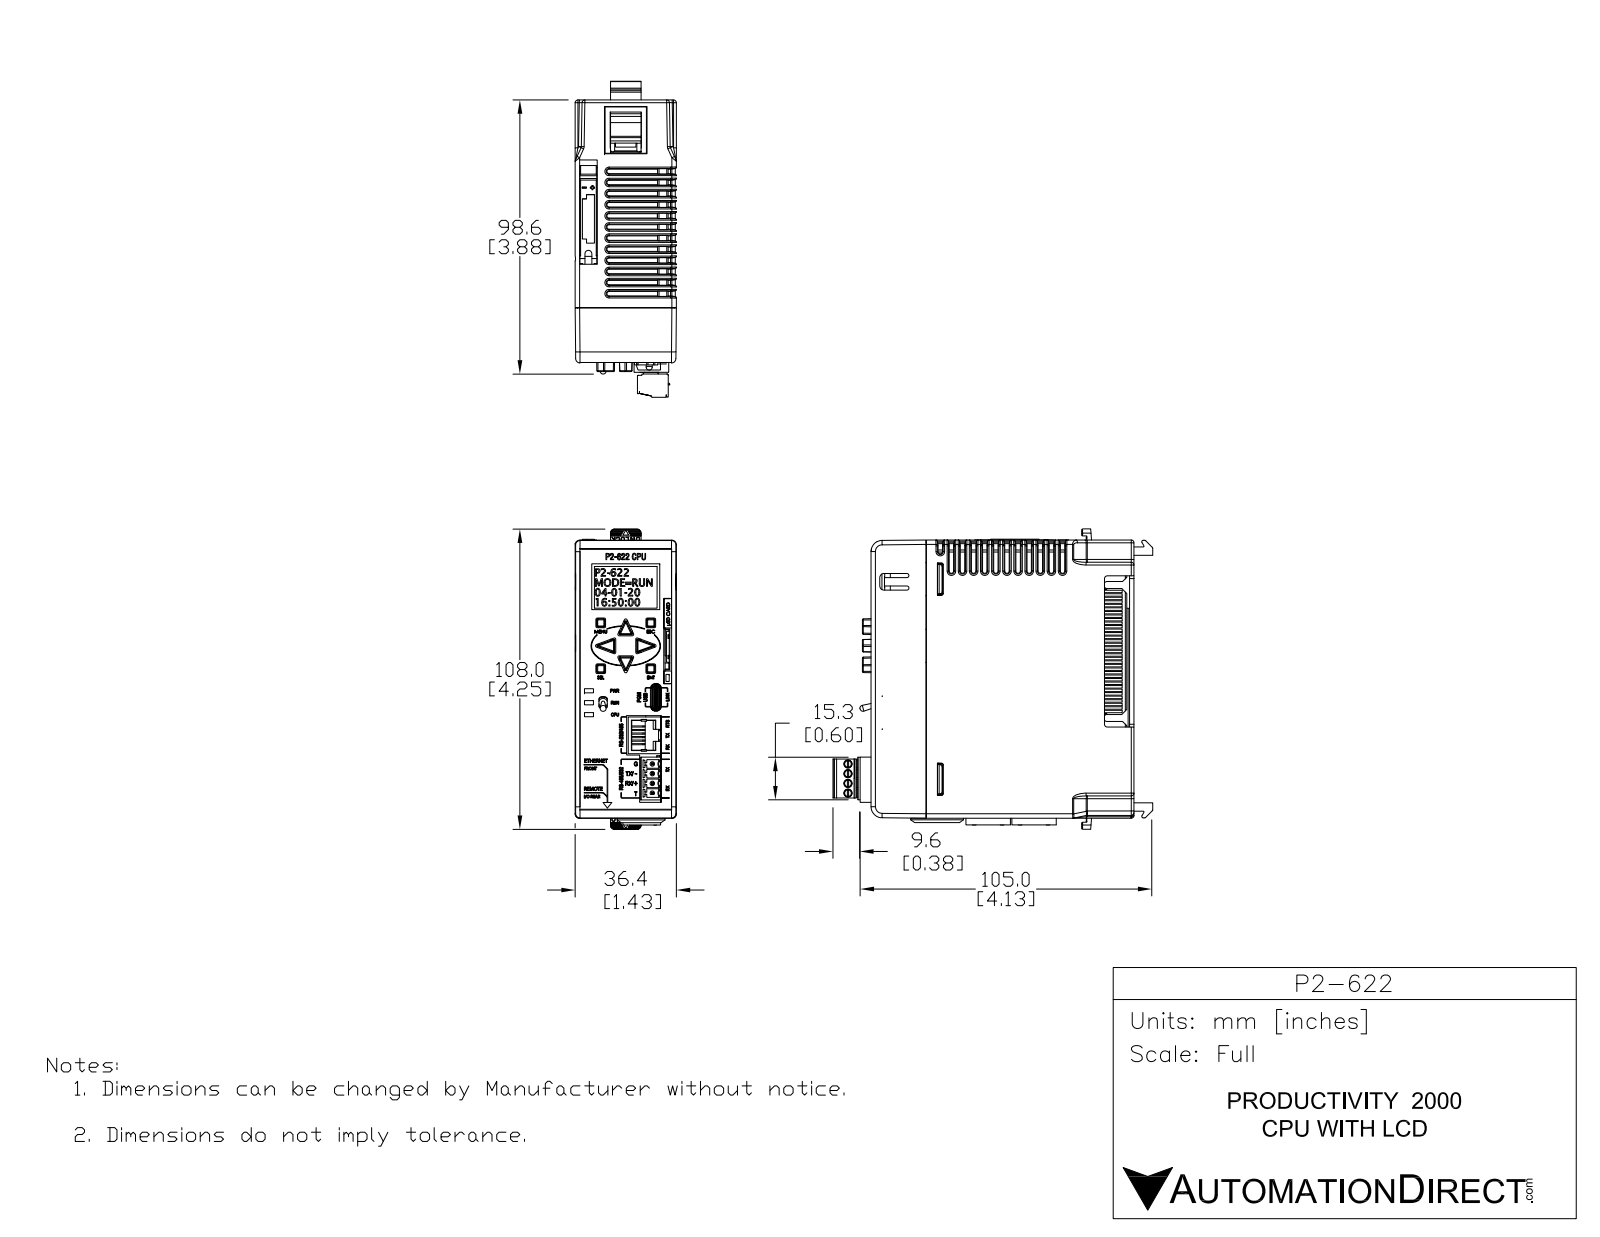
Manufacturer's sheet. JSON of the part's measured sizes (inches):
{"part_name": "P2-622 fxt", "step_written_by": "SolidWorks 2017 (AUTOMOTIVE_DESIGN)", "units": "inches", "bodies": {"solids": 9, "faces": 4031, "planar": 2741, "cylindrical": 663, "other": 627}, "overall_size": [4.253, 4.149, 1.433], "volume_in3": 16.58, "surface_area_in2": 103.4, "round_holes": [[0.01, 8], [0.016, 7], [0.079, 3], [0.02, 2], [0.028, 2], [0.039, 2], [0.059, 2], [0.083, 2], [0.087, 2], [0.123, 1]], "round_bosses_or_shafts": [[0.063, 12], [0.031, 2], [0.01, 2], [0.186, 1]], "partial_cylinders_radius": [[0.02, 200], [0.039, 81], [0.012, 38], [0.059, 18], [0.063, 15], [0.016, 12], [0.008, 8], [0.028, 8]], "face_to_face_distances": [0.063, 1.433, 1.37, 2.663, 0.863, 3.525, 0.8, 3.462, 3.714, 3.651], "hole_center_spacings": [0.332, 0.361, 0.383, 0.68, 0.717, 0.65, 0.709, 0.167]}
